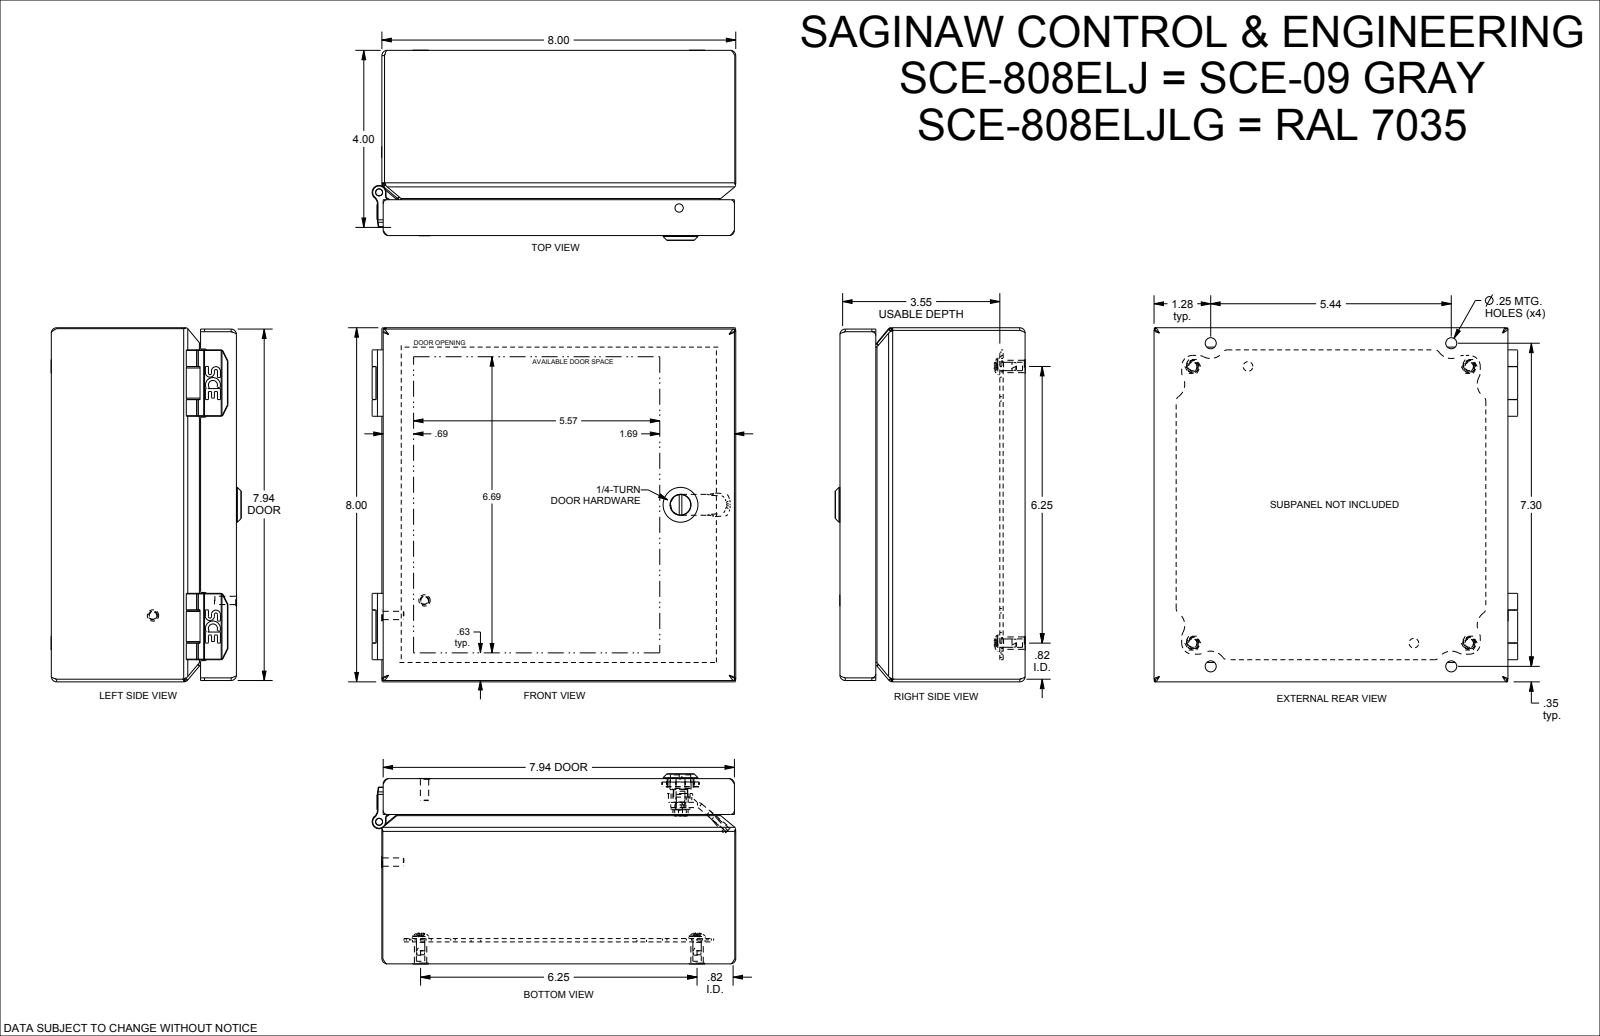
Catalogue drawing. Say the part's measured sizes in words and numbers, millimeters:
The part is named "SCE-808ELJLG". Its 3-D file was written by "SolidWorks 2019 (CONFIG_CONTROL_DESIGN)". It is 0 solids with 2654 faces: 858 planar, 764 cylindrical and 1032 other. Overall it measures 208.8 by 203.2 by 109.1 millimeters. Round holes: 8 of diameter 6.4, 4 of diameter 4.8, 4 of diameter 7.2, 4 of diameter 12.2, 2 of diameter 0.5, 2 of diameter 2.5, 2 of diameter 4.4, 2 of diameter 5, 2 of diameter 5.5, 2 of diameter 6.8, 1 of diameter 4, 1 of diameter 4.7. Round bosses or shafts: 6 of diameter 4.8, 4 of diameter 9.5, 4 of diameter 7.1, 4 of diameter 4.3, 4 of diameter 4.1, 4 of diameter 3.4, 4 of diameter 2.7, 2 of diameter 6.6. Partial cylindrical surfaces (rounded edges, fillets, slot ends): 132 of radius 2.7, 131 of radius 0.1, 32 of radius 0.2, 26 of radius 0.3, 24 of radius 0.6, 24 of radius 0.8, 22 of radius 1.5, 21 of radius 0.3. The main face-to-face distances are 1.5, 201.7, 1.5, 104.7, 103.3, 106.3, 104.8, 14.5, 13, 90.3. The hole center spacings are 16.9, 149, 158.8, 172.4, 227.3, 25.2, 31.8, 80.
